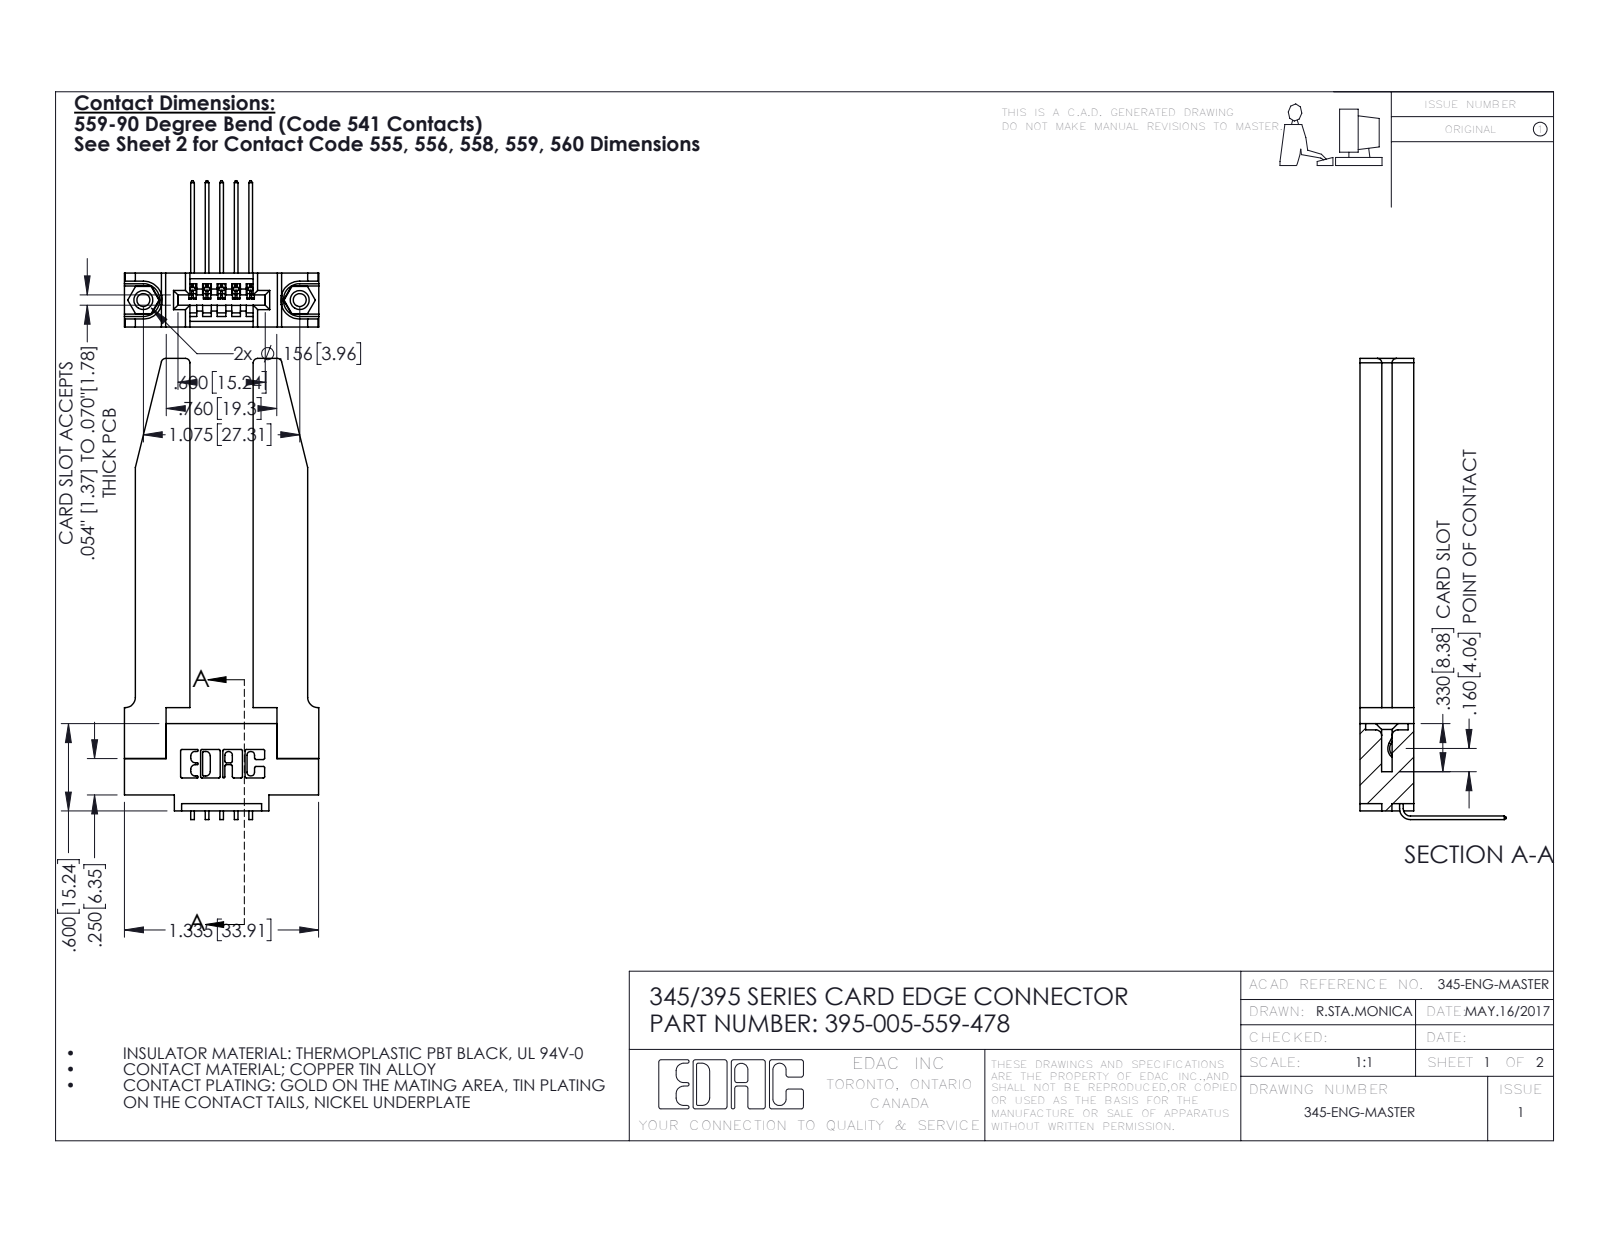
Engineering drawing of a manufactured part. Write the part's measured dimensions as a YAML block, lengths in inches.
part_name: "345-292-001_558 559 Tail - 1; 395-005-559-478; 345-220-078_345-220-078; 345 Part_0.110 Offset - 0.156 Dia-TH (+1 more)"
step_written_by: "SolidWorks 2016 (CONFIG_CONTROL_DESIGN)"
units: inches
bodies: {solids: 10, faces: 664, planar: 436, cylindrical: 176, other: 52}
overall_size: [3.169, 1.336, 1.005]
volume: 0.649
surface_area: 16.01
round_holes:
  - {diameter: 0.089, count: 2}
  - {diameter: 0.125, count: 2}
  - {diameter: 0.156, count: 2}
  - {diameter: 0.064, count: 1}
round_bosses_or_shafts:
  - {diameter: 0.155, count: 2}
partial_cylinders:
  - {radius: 0.01, count: 22}
  - {radius: 0.006, count: 10}
  - {radius: 0.03, count: 8}
  - {radius: 0.007, count: 6}
  - {radius: 0.031, count: 6}
  - {radius: 0.026, count: 3}
  - {radius: 0.031, count: 2}
  - {radius: 0.04, count: 2}
face_to_face_distances: [0.37, 0.15, 0.22, 0.435, 0.072, 0.148, 0.298, 0.077, 0.071, 0.055]
hole_center_spacings: [0.27, 0.847, 1.075]
